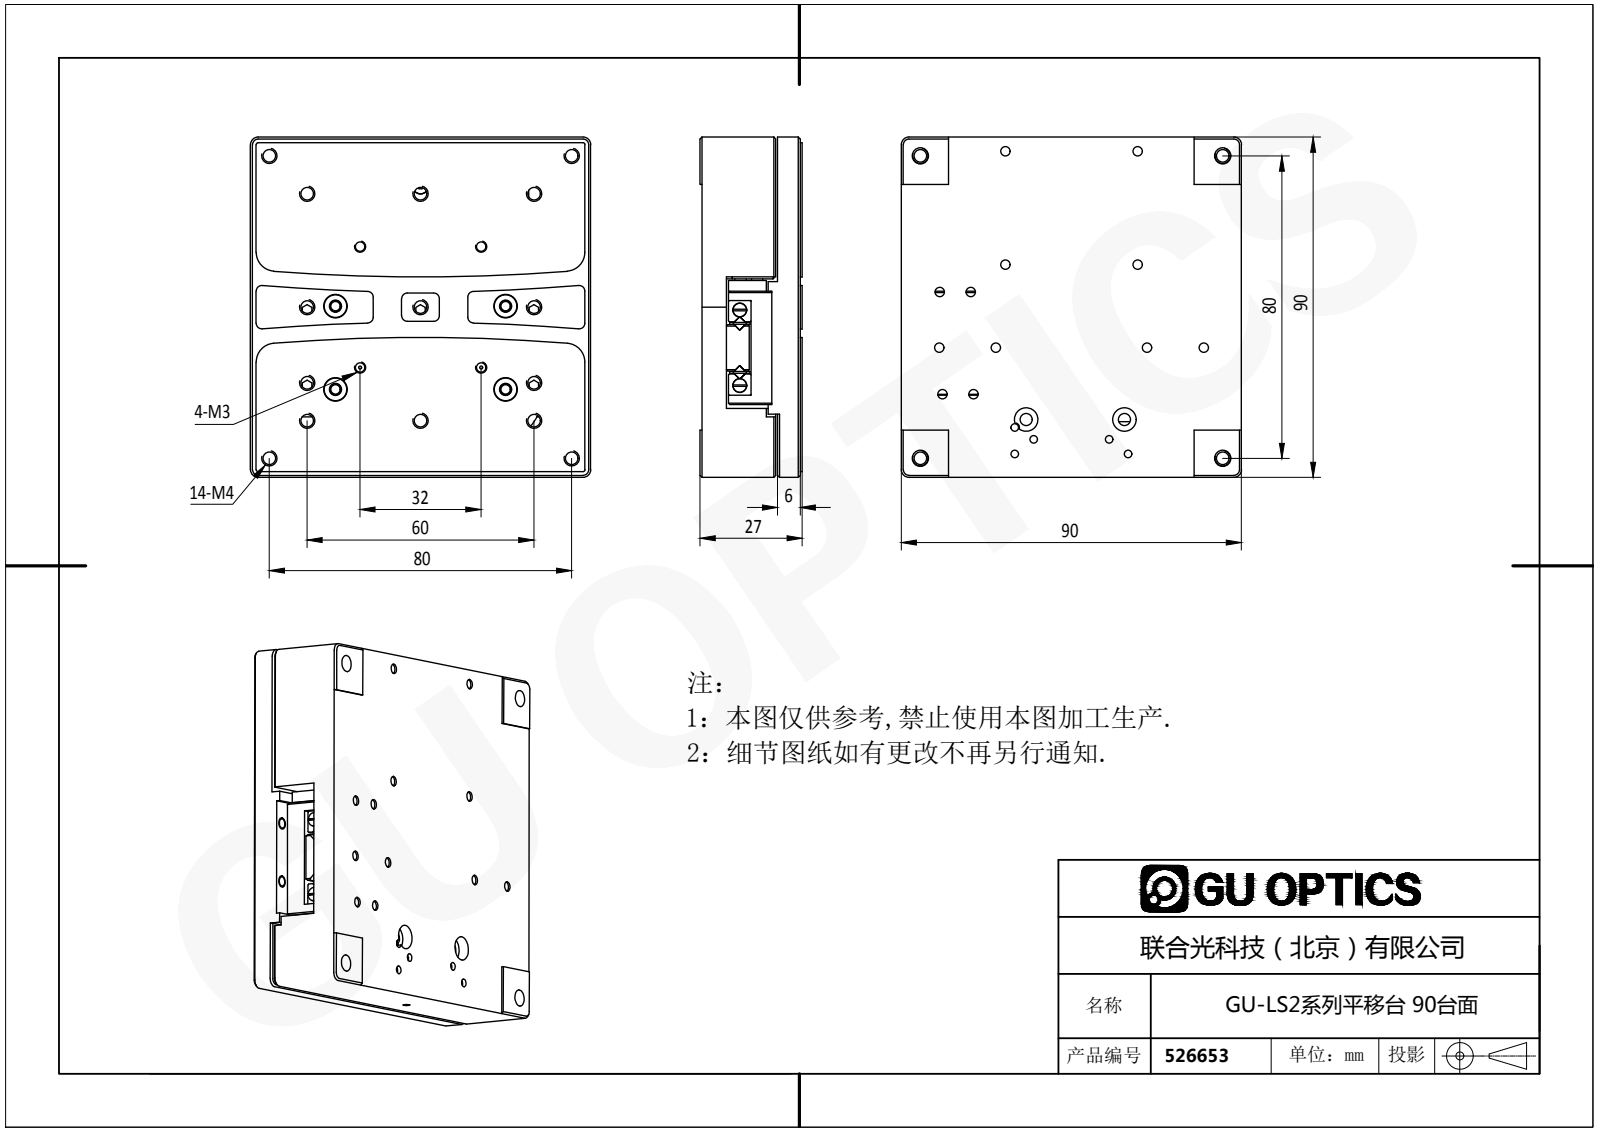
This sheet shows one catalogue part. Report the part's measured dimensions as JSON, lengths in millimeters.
{"part_name": "GU-LS2系列平移台 90台面", "step_written_by": "SolidWorks 2016 (CONFIG_CONTROL_DESIGN)", "units": "millimeters", "bodies": {"solids": 11, "faces": 1135, "planar": 535, "cylindrical": 335, "other": 265}, "overall_size": [90, 90, 27], "volume_mm3": 162553, "surface_area_mm2": 67425, "round_holes": [[2.5, 21], [3.3, 15], [6, 14], [4.5, 10], [3.2, 6], [6.2, 6], [1.57, 5], [2.05, 5], [2.46, 4], [3.5, 4], [4.3, 4], [8.25, 4]], "round_bosses_or_shafts": [[5.5, 10], [3, 10], [7.53, 4], [4, 4]], "partial_cylinders_radius": [[1.5, 16], [3, 12], [2, 9], [0.5, 7], [2.5, 6], [5, 4], [1, 2], [3.2, 2]], "face_to_face_distances": [6.5, 20, 0.5, 13.5, 26.5, 7, 13, 6, 1.5, 18.5], "hole_center_spacings": [15, 30, 7.57, 11.18, 22.3, 22.36, 25, 36.4]}
